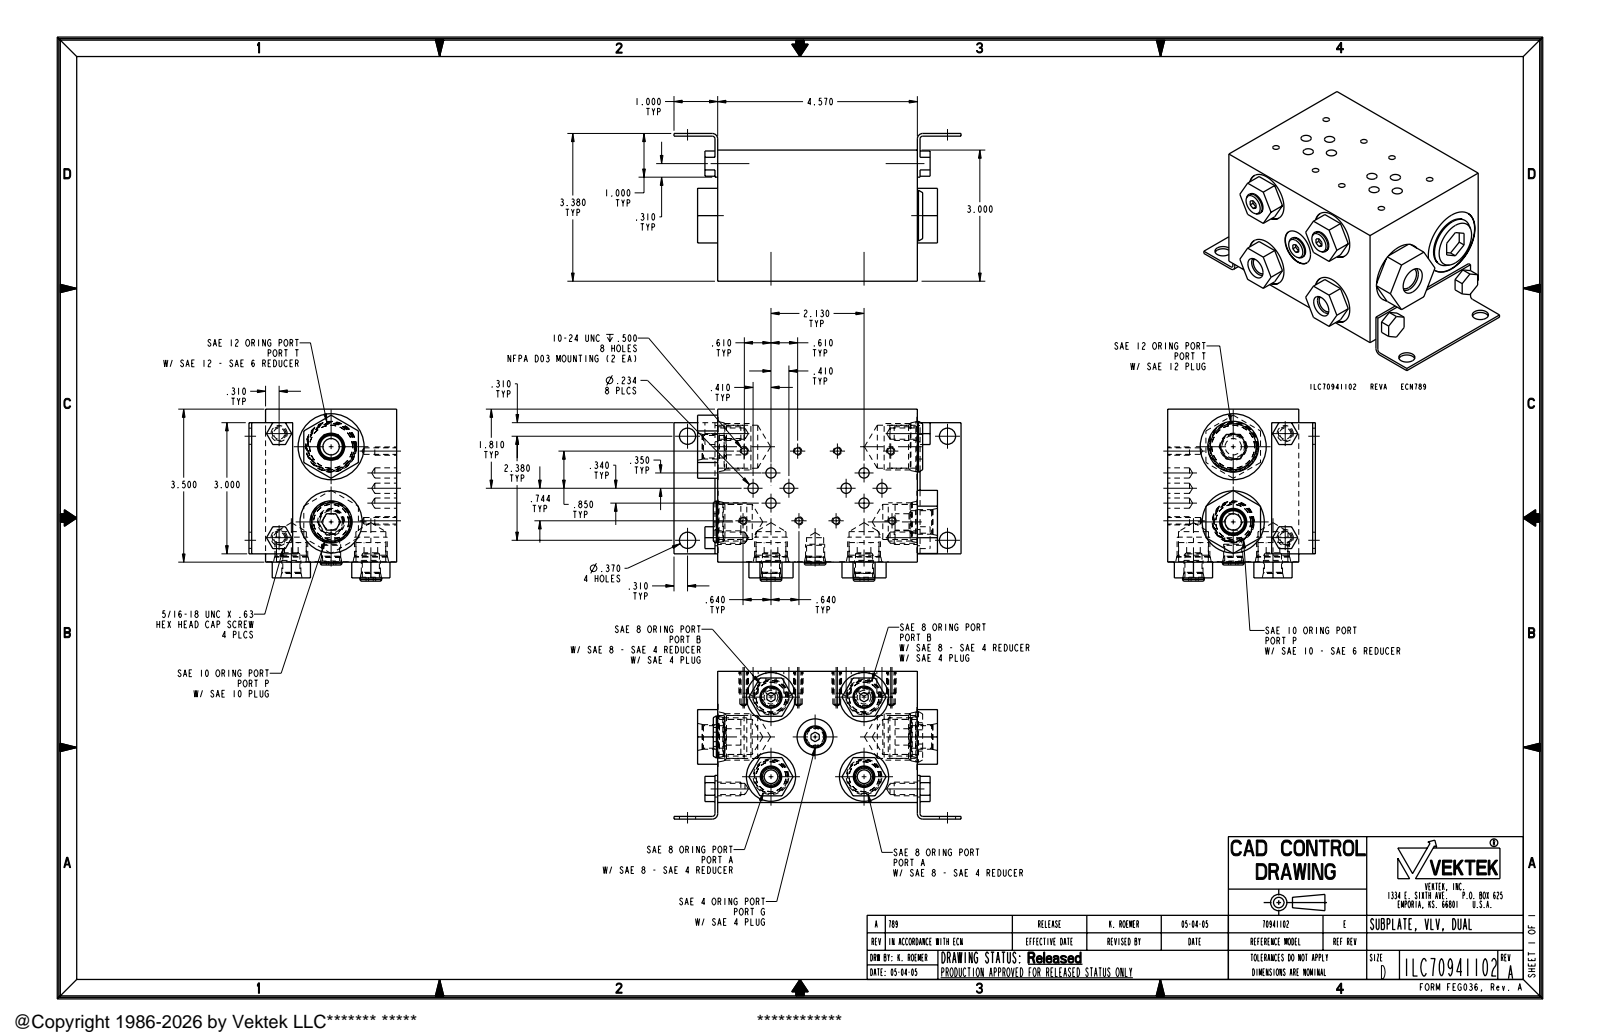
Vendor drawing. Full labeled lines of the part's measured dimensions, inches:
Part name (STEP PRODUCT): ILC70941102
STEP written by: PRO/ENGINEER BY PARAMETRIC TECHNOLOGY CORPORATION, 2004290 (AUTOMOTIVE_DESIGN_CC2)
Units: inches
Bodies: 6 solids, 551 faces (201 planar, 200 cylindrical, 150 other)
Overall size (bounding box): 6.57 × 3.935 × 3.38
Volume: 48.44 in³ · Surface area: 182.7 in²
Round holes (diameter × count): ⌀0.15 ×8, ⌀0.19 ×8, ⌀0.234 ×8, ⌀0.37 ×6, ⌀0.392 ×5, ⌀0.312 ×4, ⌀0.686 ×4, ⌀1.125 ×4, ⌀0.257 ×2, ⌀0.313 ×2, ⌀0.375 ×2, ⌀0.515 ×2
Round bosses / shafts (diameter × count): ⌀0.75 ×4, ⌀0.68 ×4, ⌀0.437 ×4, ⌀0.39 ×3, ⌀0.563 ×2, ⌀1.063 ×1, ⌀0.98 ×1, ⌀0.875 ×1
Partial cylindrical surfaces — rounded edges, fillets, slot ends (radius × count): R0.062 ×2, R0.124 ×2
Main face-to-face distances: 3, 0.062, 3.5, 4.57, 0.38, 3.38, 0.318, 3.318, 4.632, 0.36
Hole centre spacings: 2.13, 0.779, 0.873, 1.287, 1.337, 1.594, 1.915, 2.026
